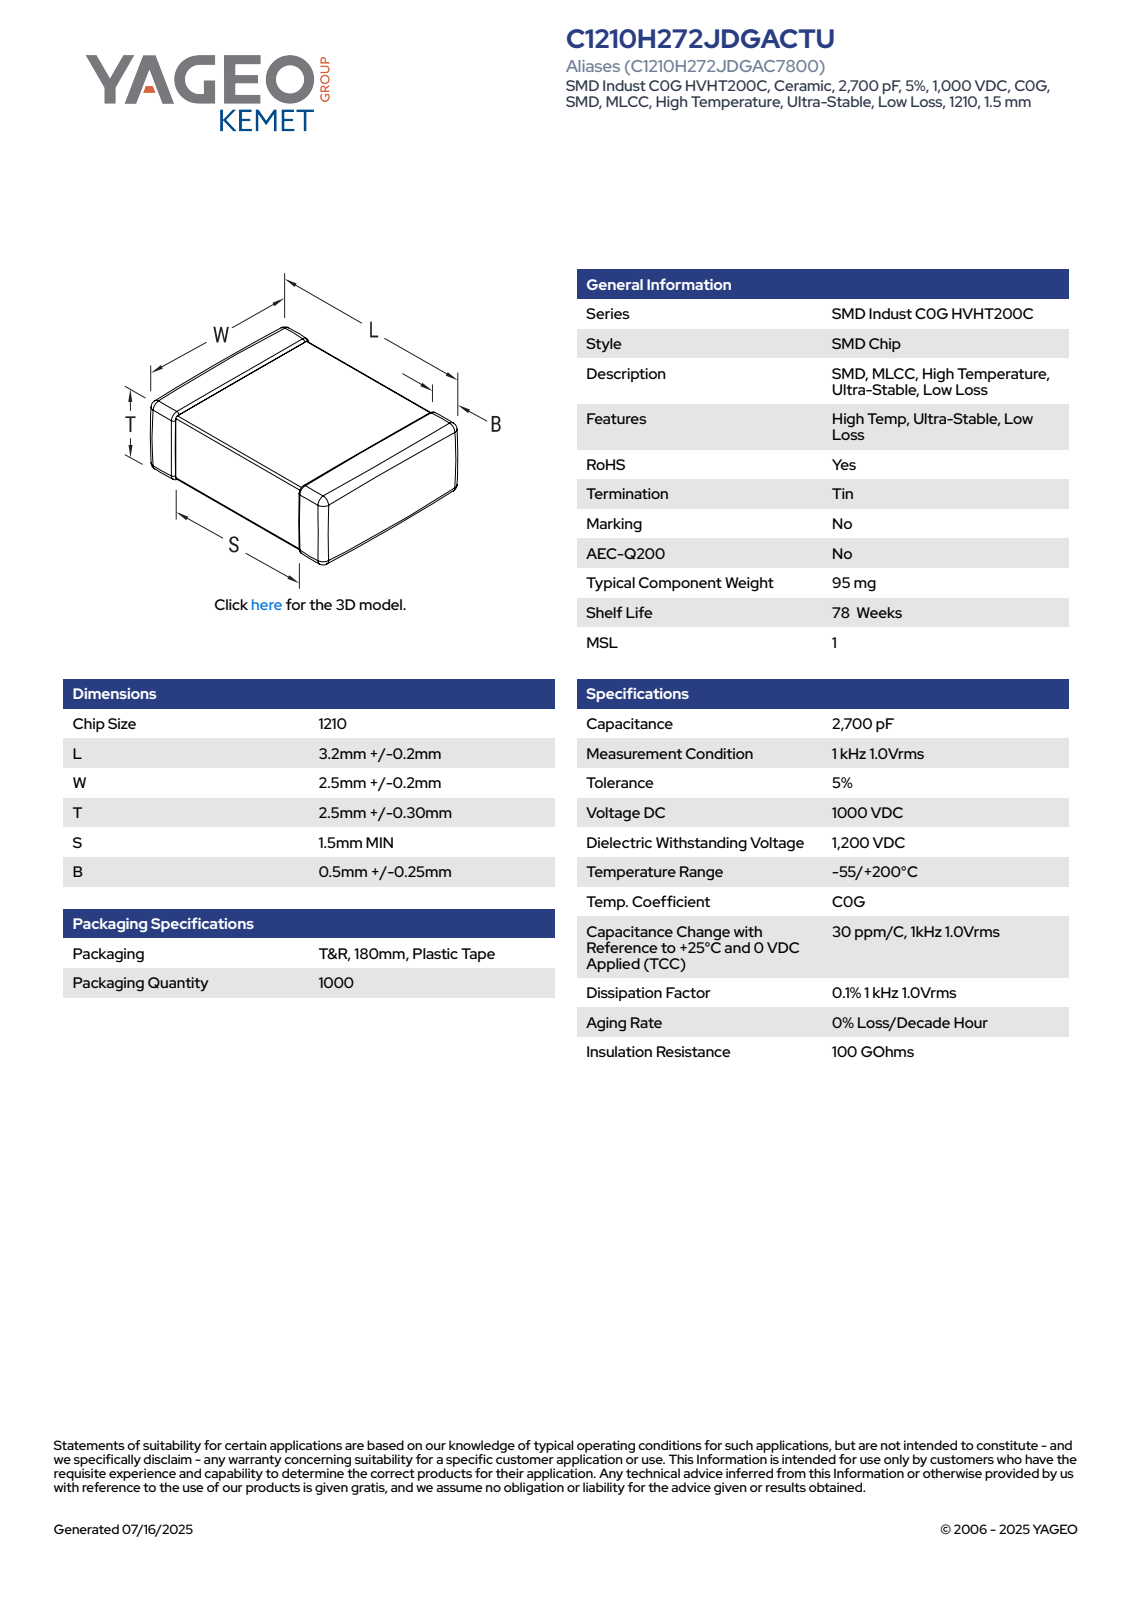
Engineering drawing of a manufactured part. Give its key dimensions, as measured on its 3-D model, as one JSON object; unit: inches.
{"part_name": "CCS_CCSTDNOS_1210_L3.4W2.7T2.8B0.75", "step_written_by": "SolidWorks 2014 (AUTOMOTIVE_DESIGN)", "units": "inches", "bodies": {"solids": 4, "faces": 125, "planar": 71, "cylindrical": 38, "other": 16}, "overall_size": [0.134, 0.11, 0.106], "volume_in3": 0.002, "surface_area_in2": 0.081, "face_to_face_distances": [0.134, 0.104, 0.108, 0.102, 0.106, 0.106, 0.11, 0.108, 0.106, 0.052]}
